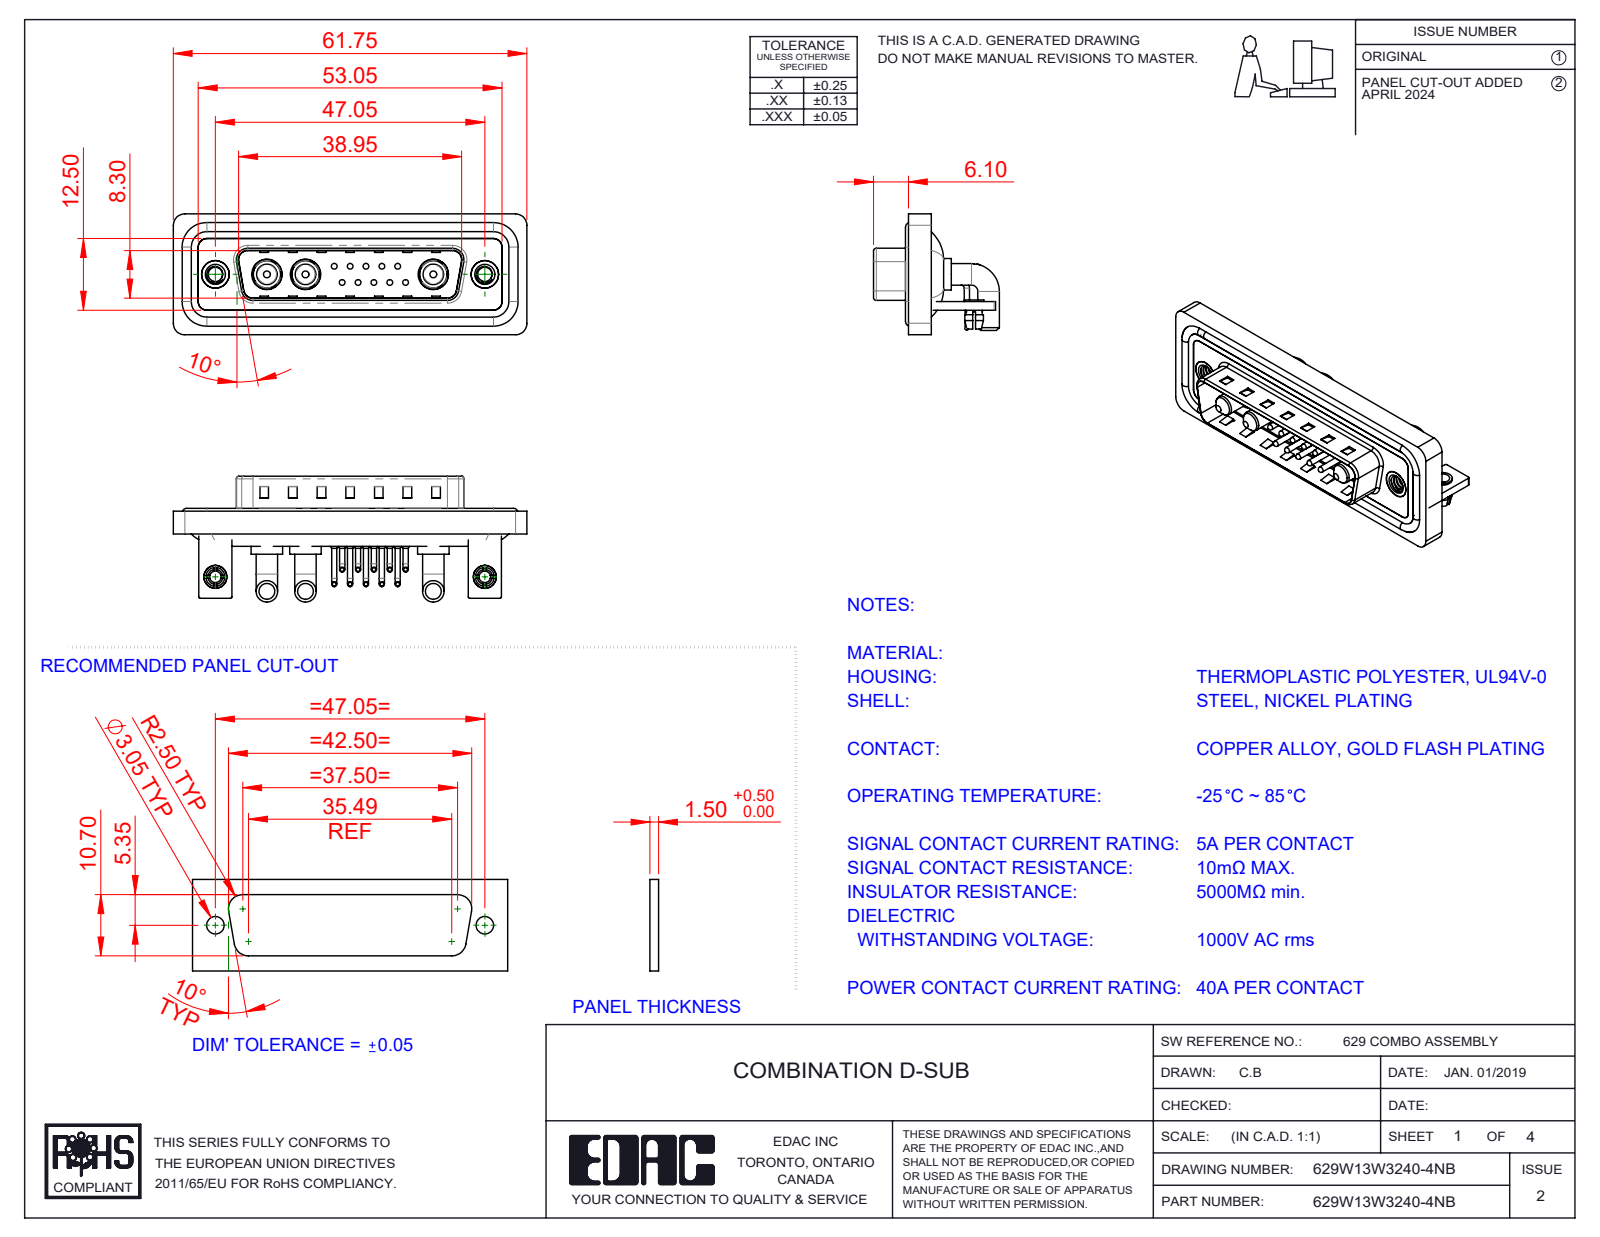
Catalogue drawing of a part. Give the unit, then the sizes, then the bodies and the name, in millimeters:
Units: millimetres
Overall size (bounding box): 61.75 × 21.98 × 21.1
Round holes (diameter × count): ⌀2 ×12, ⌀0.75 ×10, ⌀1.6 ×10, ⌀2.5 ×4, ⌀4.85 ×3, ⌀5.3 ×3, ⌀3.2 ×2, ⌀4 ×2, ⌀4.8 ×2, ⌀5 ×2
Round bosses / shafts (diameter × count): ⌀0.9 ×20, ⌀1.5 ×10, ⌀1 ×10, ⌀0.65 ×10, ⌀3.75 ×6, ⌀1.6 ×4, ⌀5.5 ×3, ⌀5.2 ×3
Partial cylindrical surfaces — rounded edges, fillets, slot ends (radius × count): R2 ×19, R1.5 ×18, R0.25 ×16, R1.01 ×10, R0.5 ×9, R1.6 ×8, R0.6 ×4, R0.65 ×4
Main face-to-face distances: 0.4, 0.8, 1.5, 2.9, 2.1, 1.1, 4.1, 1.6, 3.7, 4.5
Hole centre spacings: 3.16, 2.77, 5.04, 5.54, 7.49, 5.03, 8.31, 10.11
Volume: 8 137 mm³ · Surface area: 13 427 mm²
Bodies: 27 solids, 1842 faces (947 planar, 661 cylindrical, 234 other)
Part name (STEP PRODUCT): 629Combo Housing_13W3; 629Combo Waterproof Housing_25 Contacts; 629Combo Board Lock; 629Combo Contact Row 1 (+7 more)
STEP written by: SolidWorks 2023 (CONFIG_CONTROL_DESIGN)
